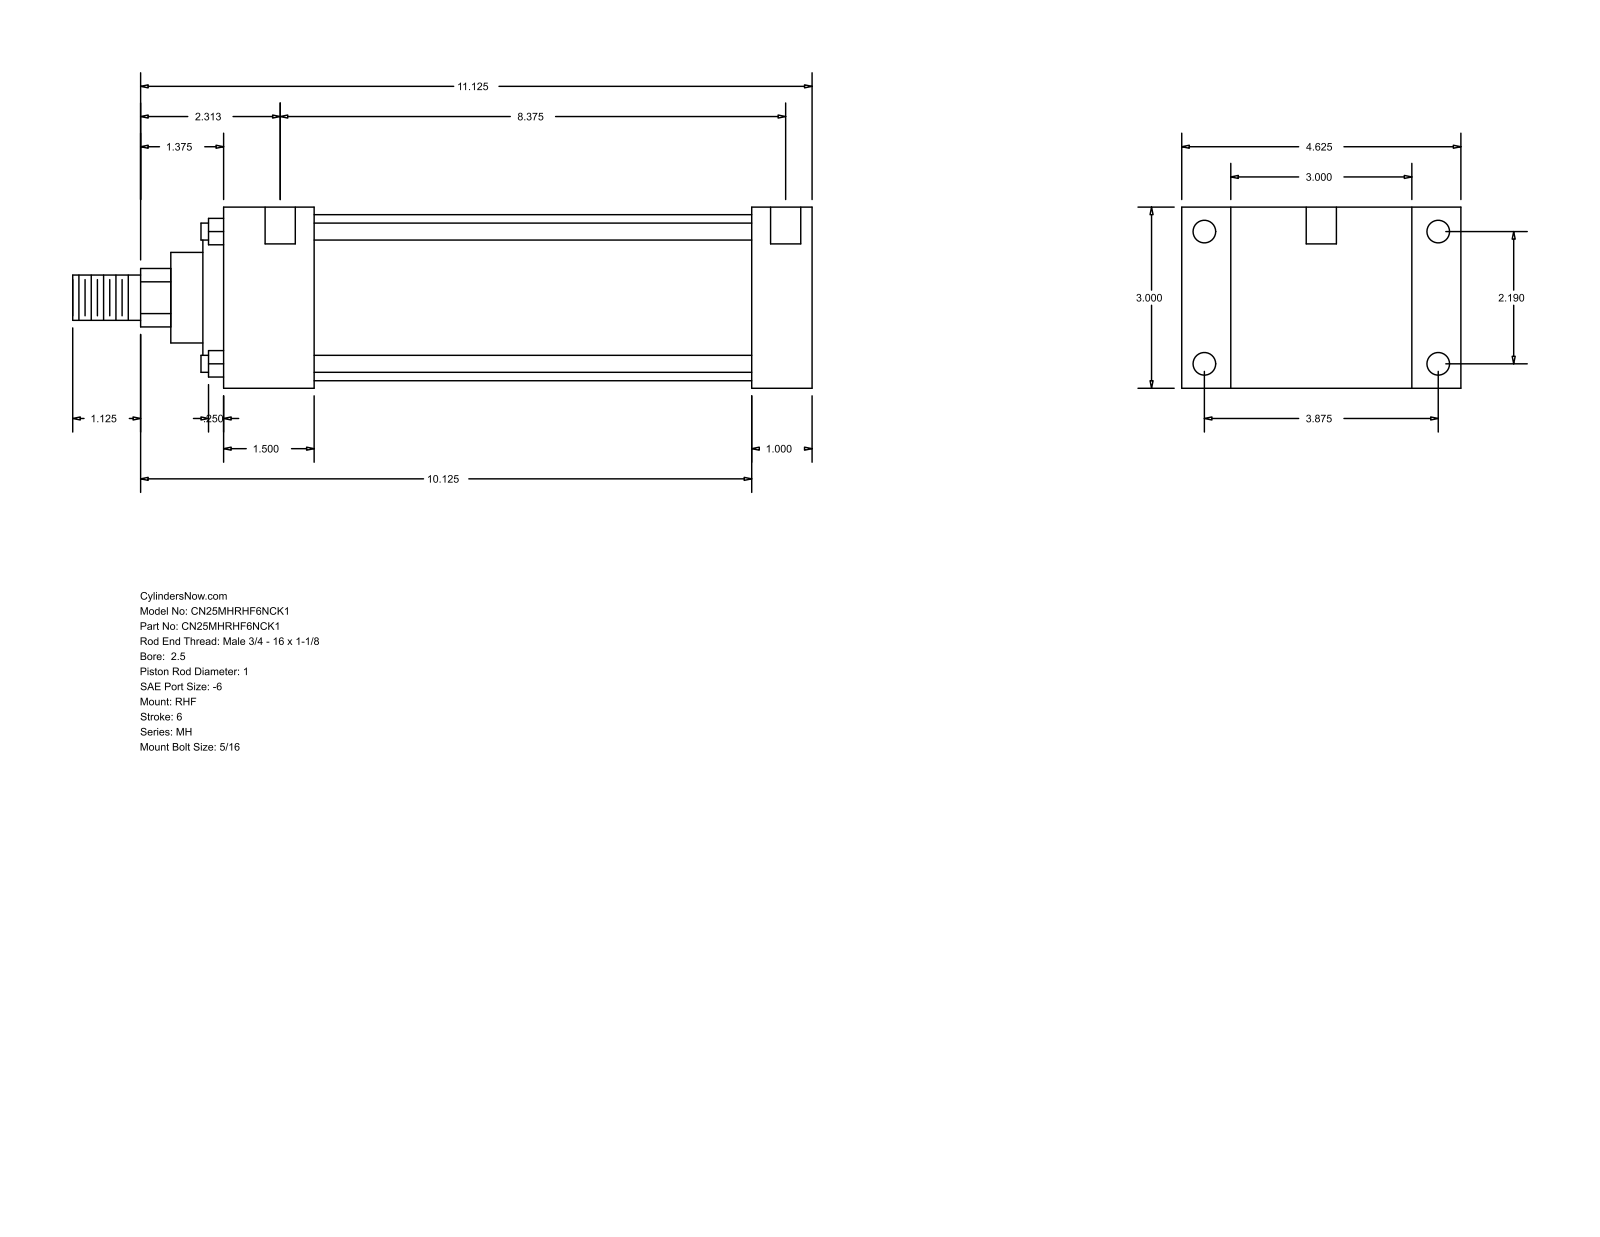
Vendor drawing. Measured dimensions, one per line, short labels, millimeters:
name: MH_RHF__0250_1
written by: GSSL Pune (CONFIG_CONTROL_DESIGN)
unit: mm
bodies: 0 solids, 90 faces (61 planar, 29 cylindrical, 0 other)
size: 311.15 × 117.47 × 76.2
holes: 4× ⌀5.56, 4× ⌀9.53, 2× ⌀12.7
bosses: 4× ⌀7.14, 1× ⌀69.85, 1× ⌀60.33, 1× ⌀38.1, 1× ⌀25.4, 1× ⌀19.05
rounds: 1× R12.29
face distances: 76.2, 25.39, 20.64, 96.84, 247.65, 222.26, 117.48, 38.11, 184.15, 209.54
hole spacings: 55.62, 98.42, 113.05, 220.66, 3.18, 4.76, 212.72, 215.9
